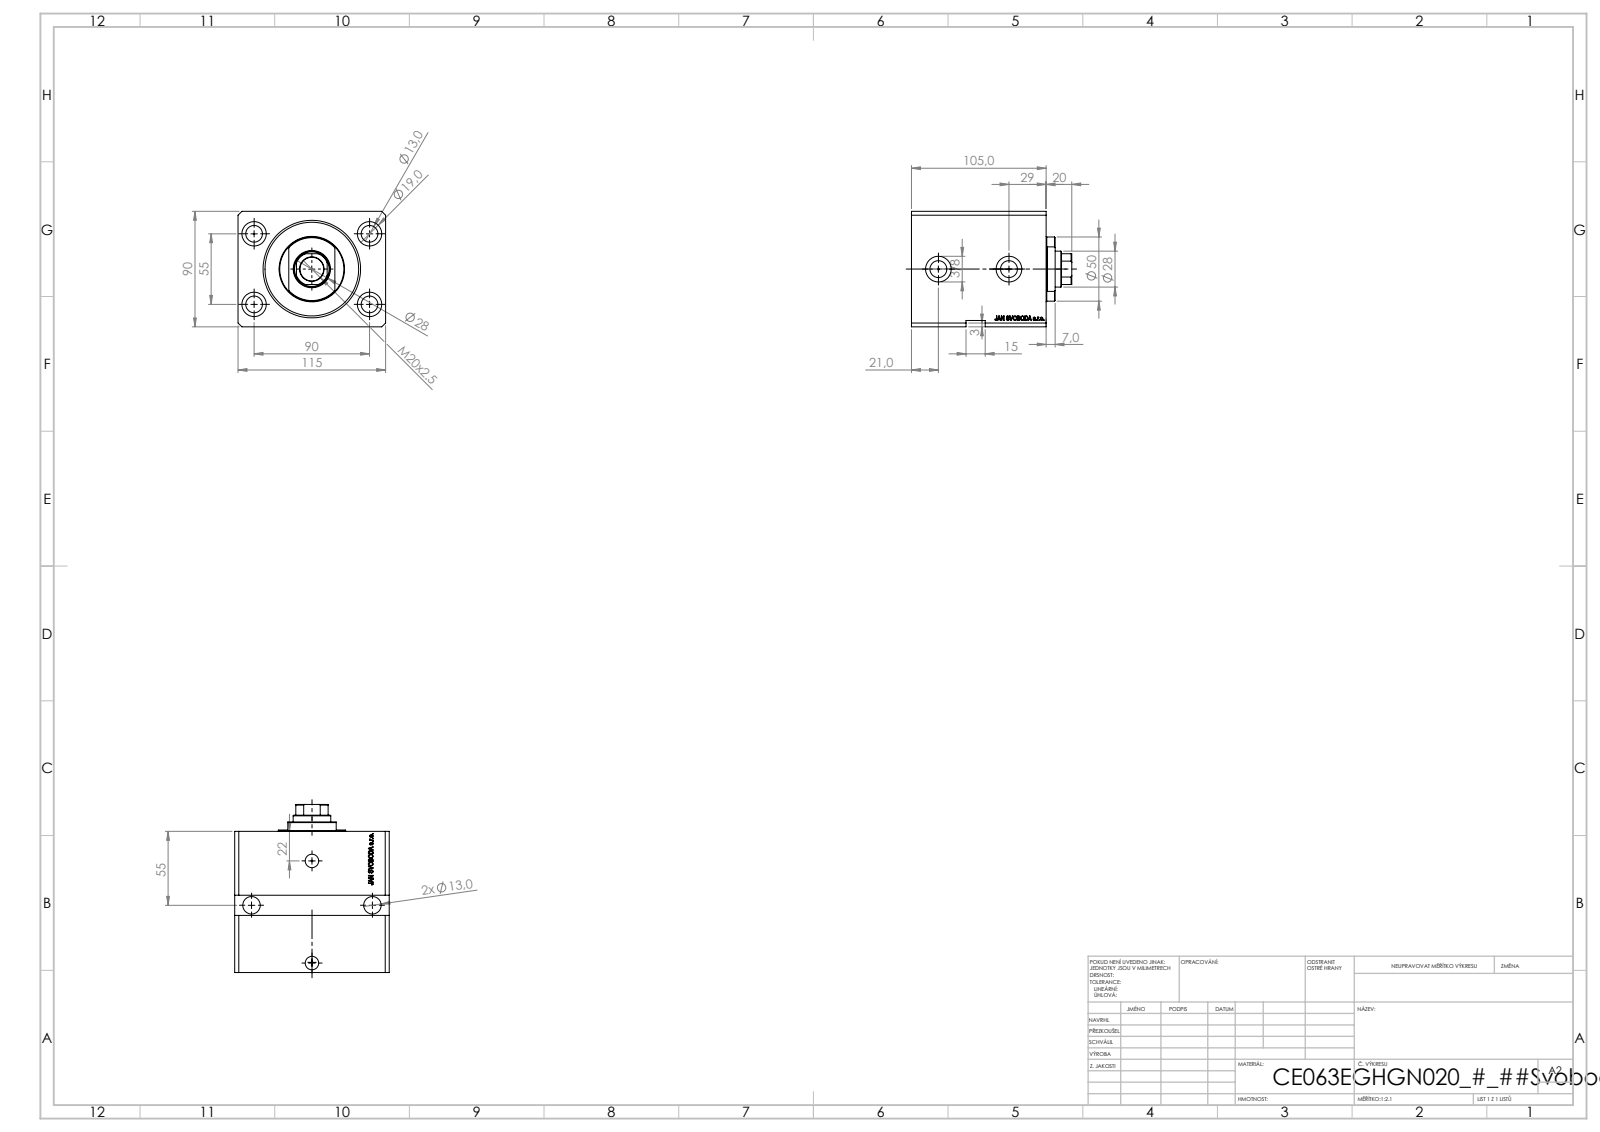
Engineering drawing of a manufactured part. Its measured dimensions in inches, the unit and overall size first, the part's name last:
Units: inches
Overall size (bounding box): 4.921 × 4.528 × 3.543
Round holes (diameter × count): ⌀0.512 ×6, ⌀0.049 ×4, ⌀0.748 ×4, ⌀0.394 ×2, ⌀0.518 ×2, ⌀0.787 ×2, ⌀0.728 ×1, ⌀1.102 ×1, ⌀2.48 ×1, ⌀2.992 ×1
Round bosses / shafts (diameter × count): ⌀1.969 ×1
Partial cylindrical surfaces — rounded edges, fillets, slot ends (radius × count): R0.531 ×1
Main face-to-face distances: 3.543, 0.787, 4.528, 3.346, 4.134, 3.429, 0.705, 2.642, 1.575, 2.559
Hole centre spacings: 2.076, 2.165, 3.543, 2.197, 2.436, 2.45, 4.153, 0.021
Volume: 57.54 in³ · Surface area: 223.5 in²
Bodies: 3 solids, 937 faces (467 planar, 84 cylindrical, 386 other)
Part name (STEP PRODUCT): V250CE_C_VCP; V250CE_E_Body; V250CE_VC_E
STEP written by: SolidWorks 2019 (CONFIG_CONTROL_DESIGN)
